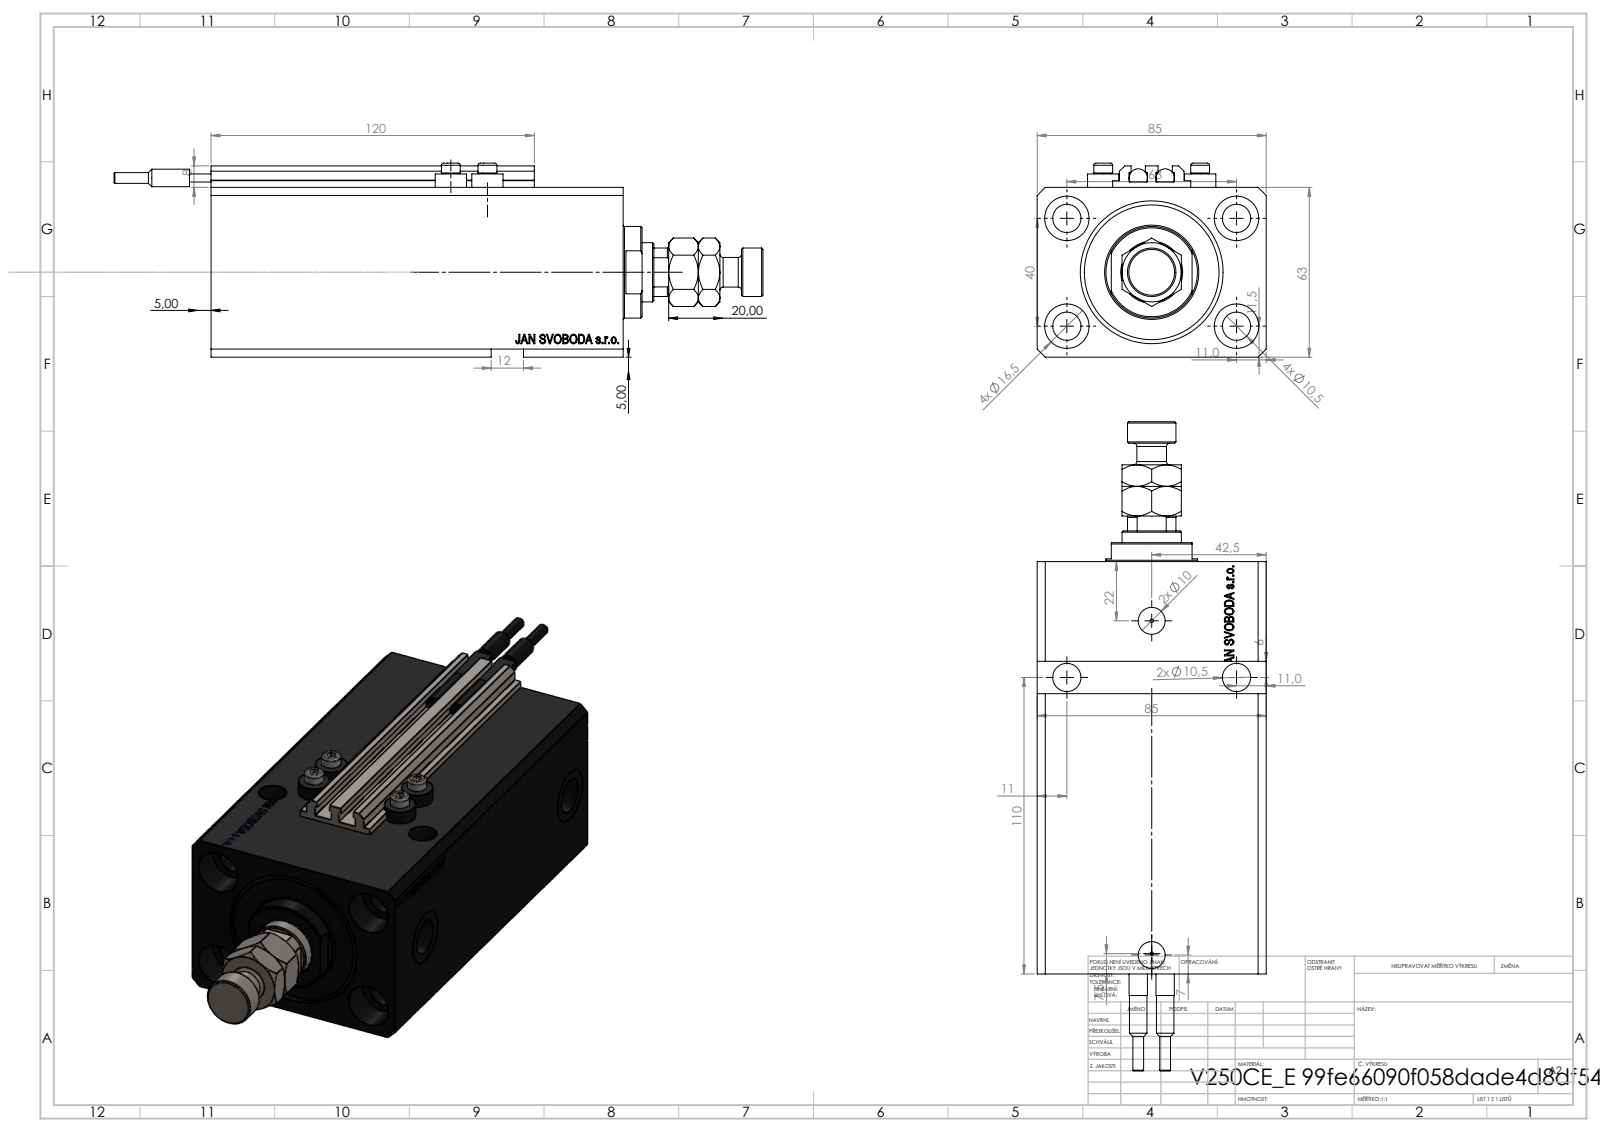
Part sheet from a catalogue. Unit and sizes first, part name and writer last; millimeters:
Units: millimetres
Overall size (bounding box): 241 × 85 × 72
Round holes (diameter × count): ⌀10.5 ×8, ⌀1.25 ×4, ⌀4 ×4, ⌀16.5 ×4, ⌀10 ×2, ⌀13.16 ×2, ⌀20 ×2, ⌀12.5 ×1, ⌀22 ×1, ⌀40 ×1, ⌀53 ×1
Round bosses / shafts (diameter × count): ⌀11.6 ×4, ⌀7 ×4, ⌀6.8 ×2, ⌀6.5 ×2, ⌀4 ×2, ⌀34 ×1, ⌀18 ×1, ⌀11 ×1
Partial cylindrical surfaces — rounded edges, fillets, slot ends (radius × count): R0.2 ×10, R10.5 ×1
Main face-to-face distances: 63, 85, 17, 153, 136, 65, 3, 11.4, 124.6, 141.6
Hole centre spacings: 37.31, 63, 13.6, 15.4, 24.96, 33.62, 36, 37.86
Volume: 698 110 mm³ · Surface area: 146 803 mm²
Bodies: 11 solids, 1211 faces (583 planar, 162 cylindrical, 466 other)
Part name (STEP PRODUCT): V250CE_C_VCP; ALLEN BOLT V250CE; SWITCH_V250CE; MFA (+2 more)
STEP written by: SolidWorks 2019 (CONFIG_CONTROL_DESIGN)
